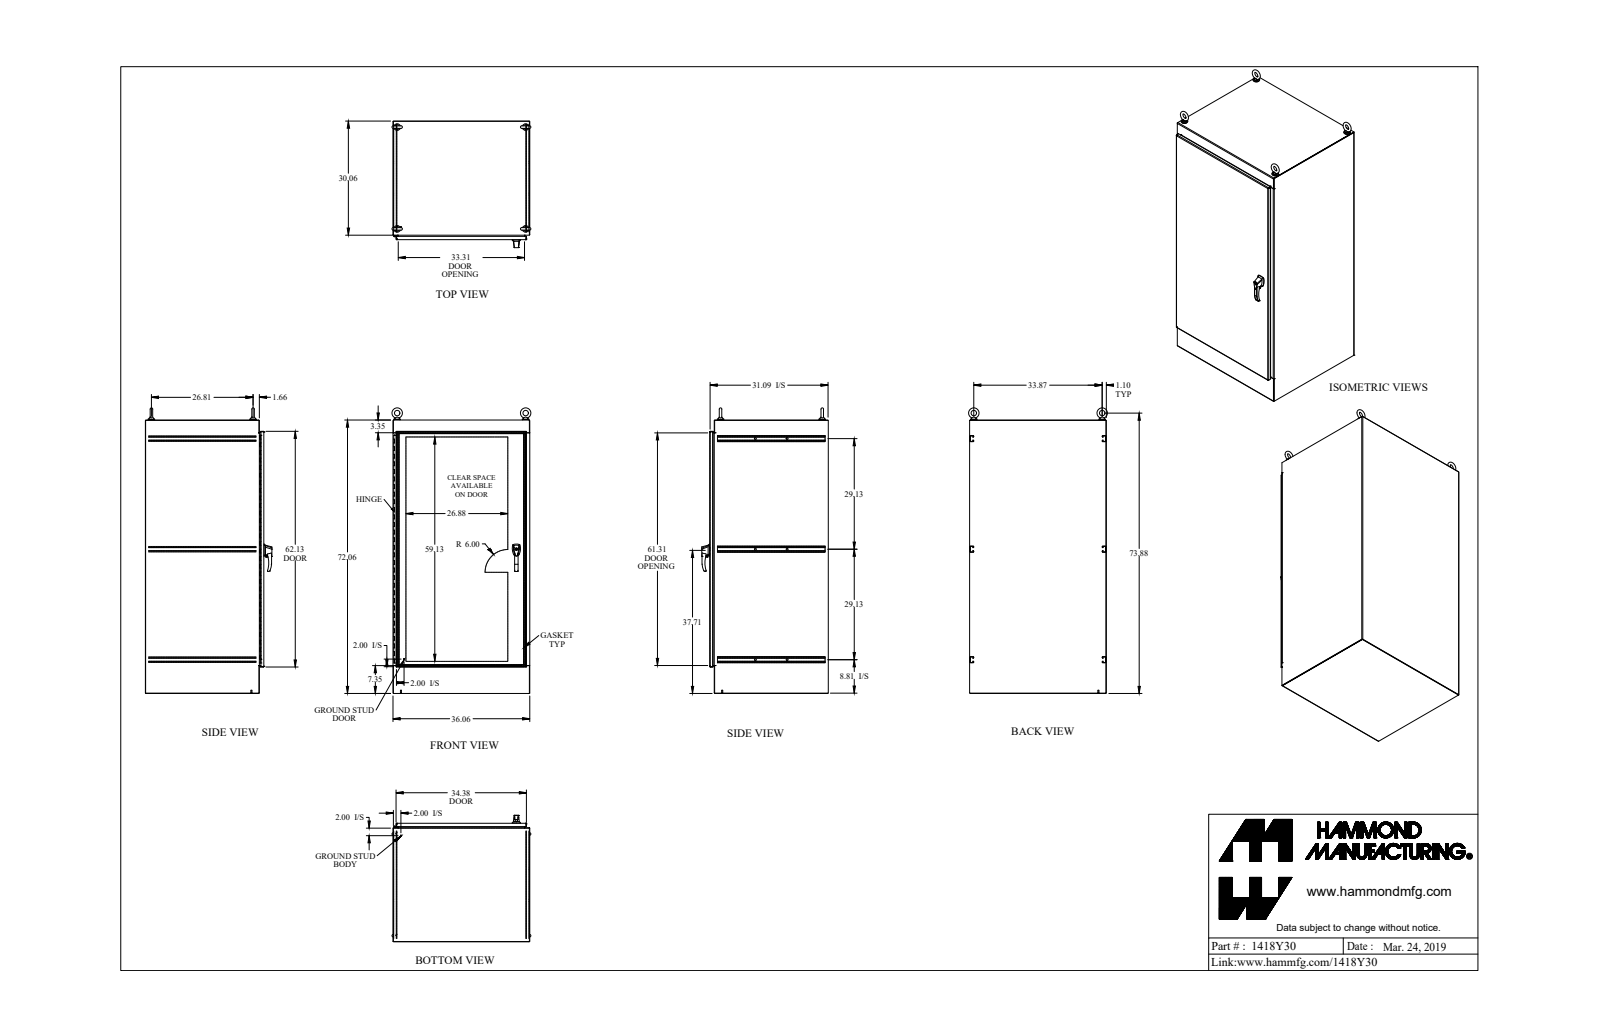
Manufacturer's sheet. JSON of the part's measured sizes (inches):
{"part_name": "1418Y30_Default", "step_written_by": "SolidWorks 2019 (CONFIG_CONTROL_DESIGN)", "units": "inches", "bodies": {"solids": 61, "faces": 1880, "planar": 813, "cylindrical": 842, "other": 225}, "overall_size": [75.713, 37.118, 33.362], "volume_in3": 1310, "surface_area_in2": 27472, "round_holes": [[0.304, 10], [0.5, 6], [0.527, 4], [0.625, 4], [0.687, 4], [0.75, 4], [0.25, 2], [0.257, 2], [0.28, 2], [0.281, 2], [0.313, 2], [0.39, 2]], "round_bosses_or_shafts": [[1.75, 4], [1.5, 4], [1.25, 4], [0.738, 4], [0.281, 4], [1, 2], [0.75, 2], [0.63, 2]], "partial_cylinders_radius": [[0.043, 42], [0.138, 36], [0.125, 22], [0.018, 16], [0.048, 13], [0.143, 13], [0.06, 10], [0.015, 8]], "face_to_face_distances": [0.095, 31.152, 35.965, 35.87, 31.057, 71.965, 36.06, 31.247, 71.87, 72.06], "hole_center_spacings": [6, 12, 18, 24, 30, 36, 8.375, 34.57]}
